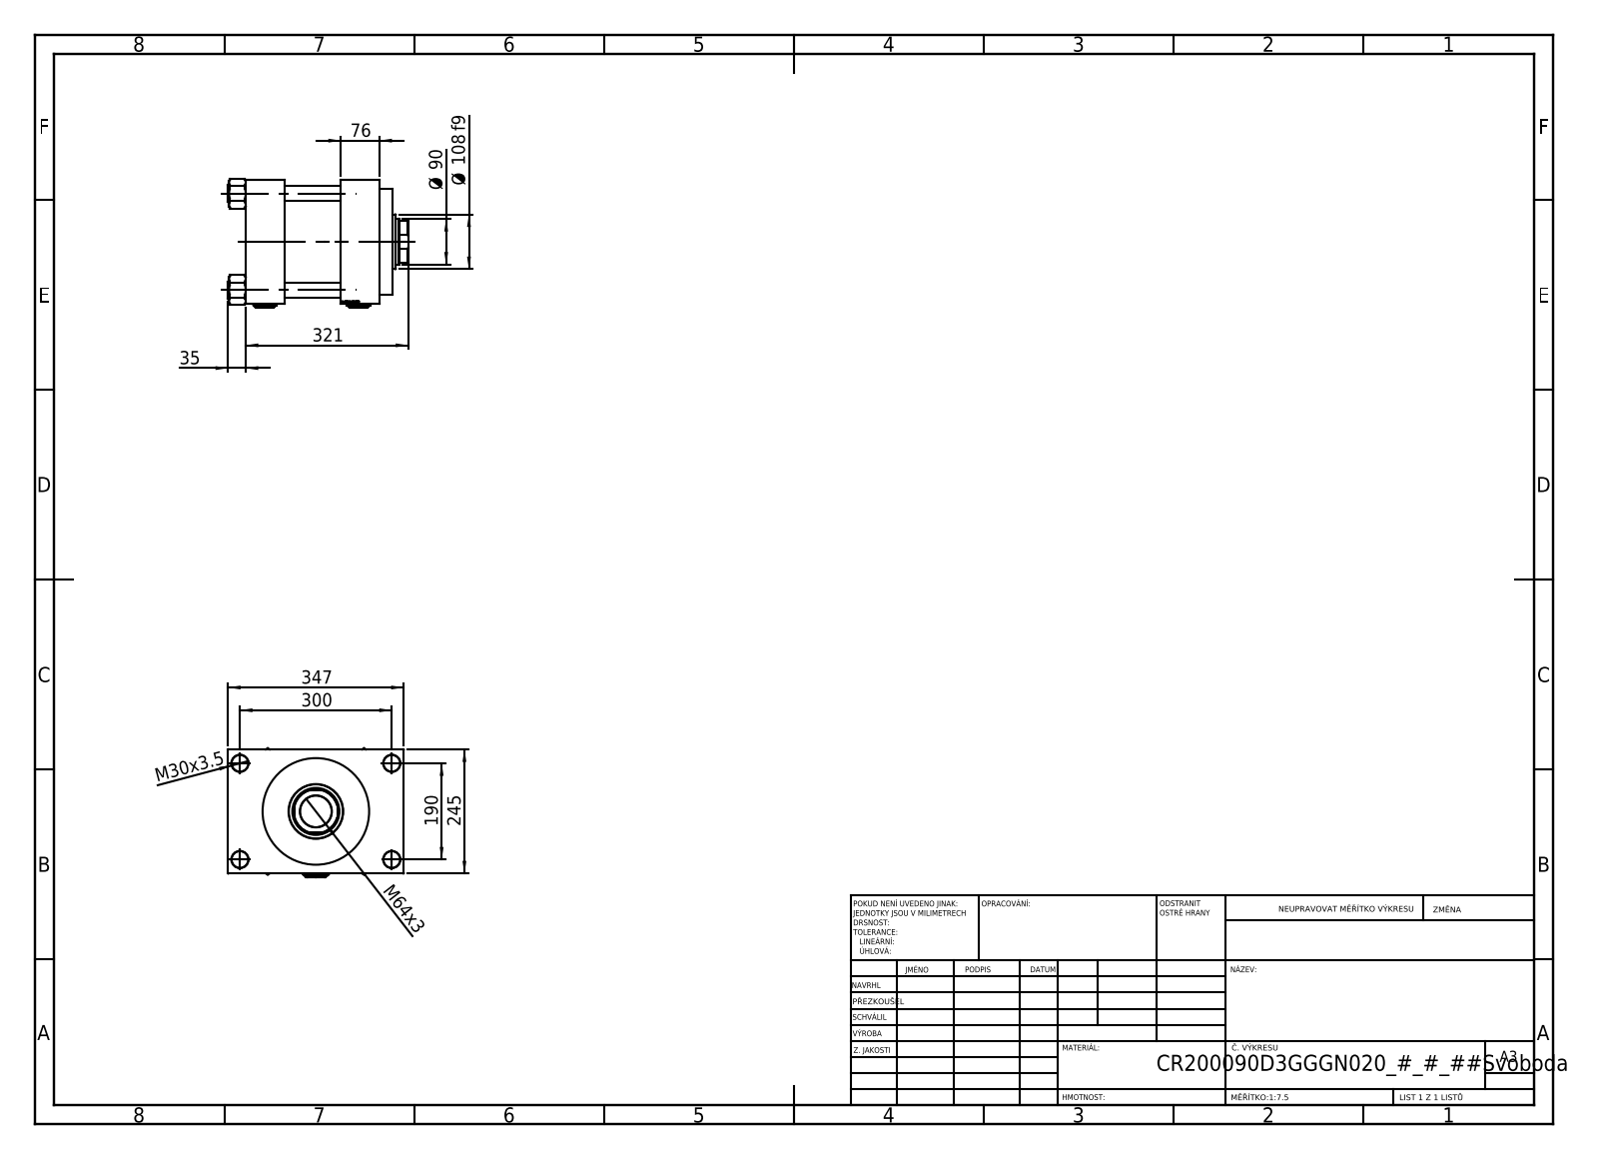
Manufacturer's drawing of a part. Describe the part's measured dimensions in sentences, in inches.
The part is named "NUT_M5_D; V215CR_VCP_D; Zatka_pro_OIL_PORT; V215CR_D_TYCINKA (+2 more)". Its 3-D file was written by "SolidWorks 2019 (CONFIG_CONTROL_DESIGN)". It is 13 solids with 1249 faces: 591 planar, 98 cylindrical and 560 other. Overall it measures 14.016 by 13.661 by 10.009 inches. Its volume is 894 cubic inches and its surface area 1 716 square inches. Round holes: 4 of diameter 1.181, 4 of diameter 1.299, 2 of diameter 0.276, 2 of diameter 1.65, 2 of diameter 2.047, 1 of diameter 2.461, 1 of diameter 3.543, 1 of diameter 3.661, 1 of diameter 5.748, 1 of diameter 7.874, 1 of diameter 8.287. Round bosses or shafts: 4 of diameter 1.299, 1 of diameter 8.11, 1 of diameter 4.252. Partial cylindrical surfaces (rounded edges, fillets, slot ends): 1 of radius 1.732. The main face-to-face distances are 2.992, 7.402, 9.646, 4.409, 10.394, 9.675, 6.683, 2.273, 0.719, 11.654. The hole center spacings are 2.161, 5.295, 6.99, 7.488, 7.79, 9.65, 12.212, 7.48.
